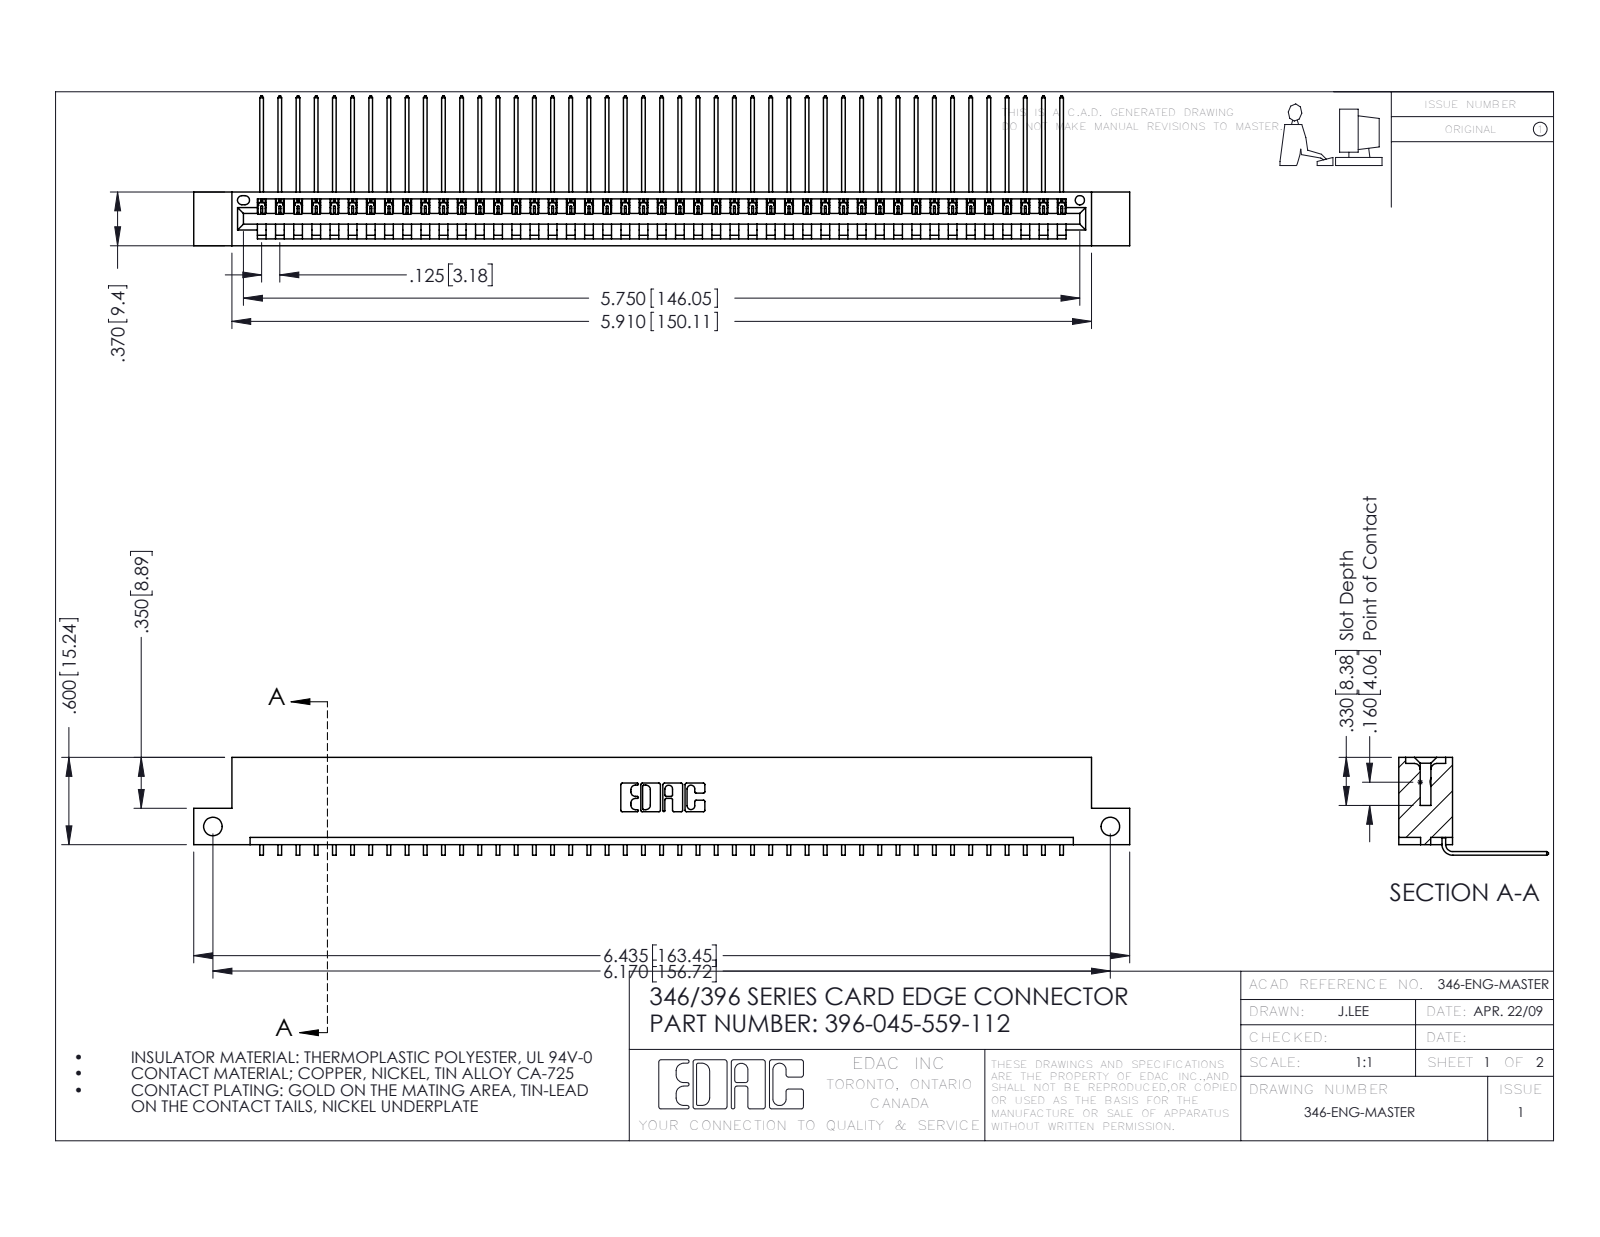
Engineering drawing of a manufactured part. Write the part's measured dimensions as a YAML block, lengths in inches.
part_name: "346 Part_Flush Mounting Lugs - Side Mount; 345-292-001_558 559 Tail - 1; 396-045-559-112"
step_written_by: "SolidWorks 2016 (CONFIG_CONTROL_DESIGN)"
units: inches
bodies: {solids: 46, faces: 2822, planar: 1966, cylindrical: 856, other: 0}
overall_size: [6.435, 1.03, 0.673]
volume: 0.96
surface_area: 31.68
round_holes:
  - {diameter: 0.128, count: 2}
  - {diameter: 0.064, count: 1}
partial_cylinders:
  - {radius: 0.006, count: 90}
  - {radius: 0.01, count: 22}
  - {radius: 0.007, count: 6}
  - {radius: 0.031, count: 6}
  - {radius: 0.026, count: 3}
  - {radius: 0.031, count: 2}
  - {radius: 0.04, count: 2}
  - {radius: 0.014, count: 1}
face_to_face_distances: [0.048, 0.322, 0.37, 0.025, 0.25, 0.072, 0.298, 0.148, 0.222, 0.1]
hole_center_spacings: [6.17]
